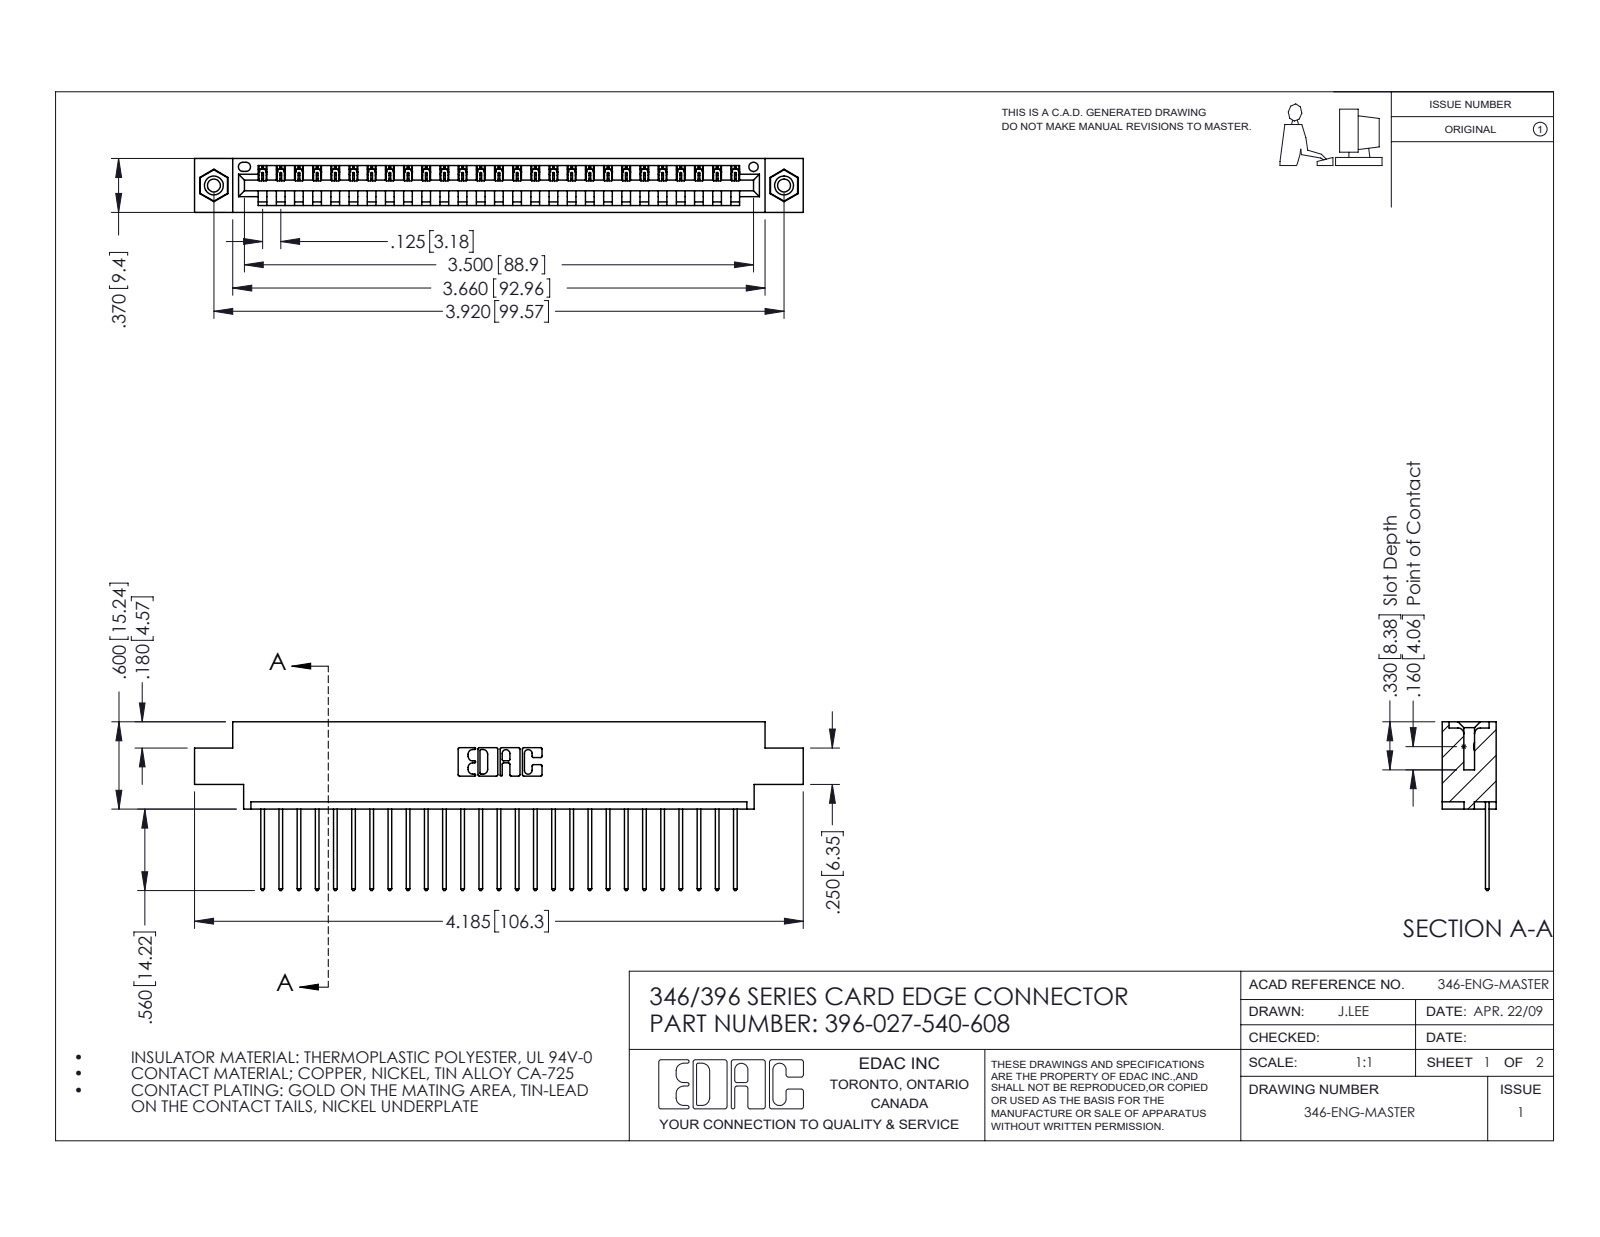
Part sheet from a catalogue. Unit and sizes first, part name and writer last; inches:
Units: inches
Overall size (bounding box): 4.185 × 1.16 × 0.37
Round holes (diameter × count): ⌀0.089 ×2, ⌀0.125 ×2, ⌀0.156 ×2, ⌀0.064 ×1
Round bosses / shafts (diameter × count): ⌀0.155 ×2
Partial cylindrical surfaces — rounded edges, fillets, slot ends (radius × count): R0.006 ×54, R0.01 ×54, R0.01 ×22, R0.007 ×6, R0.031 ×6, R0.026 ×3, R0.031 ×2, R0.04 ×2
Main face-to-face distances: 0.048, 0.322, 0.37, 0.25, 0.072, 0.298, 0.025, 0.222, 0.148, 0.1
Hole centre spacings: 0.246, 3.712, 3.92
Volume: 0.607 in³ · Surface area: 19.72 in²
Bodies: 30 solids, 1752 faces (1192 planar, 544 cylindrical, 16 other)
Part name (STEP PRODUCT): 346 Part_0.170 Offset - 0.156 Dia-TI; 396-027-540-608; 345-250-001_345-250-003-102; 345-292-001_345-293-140
STEP written by: SolidWorks 2016 (CONFIG_CONTROL_DESIGN)
